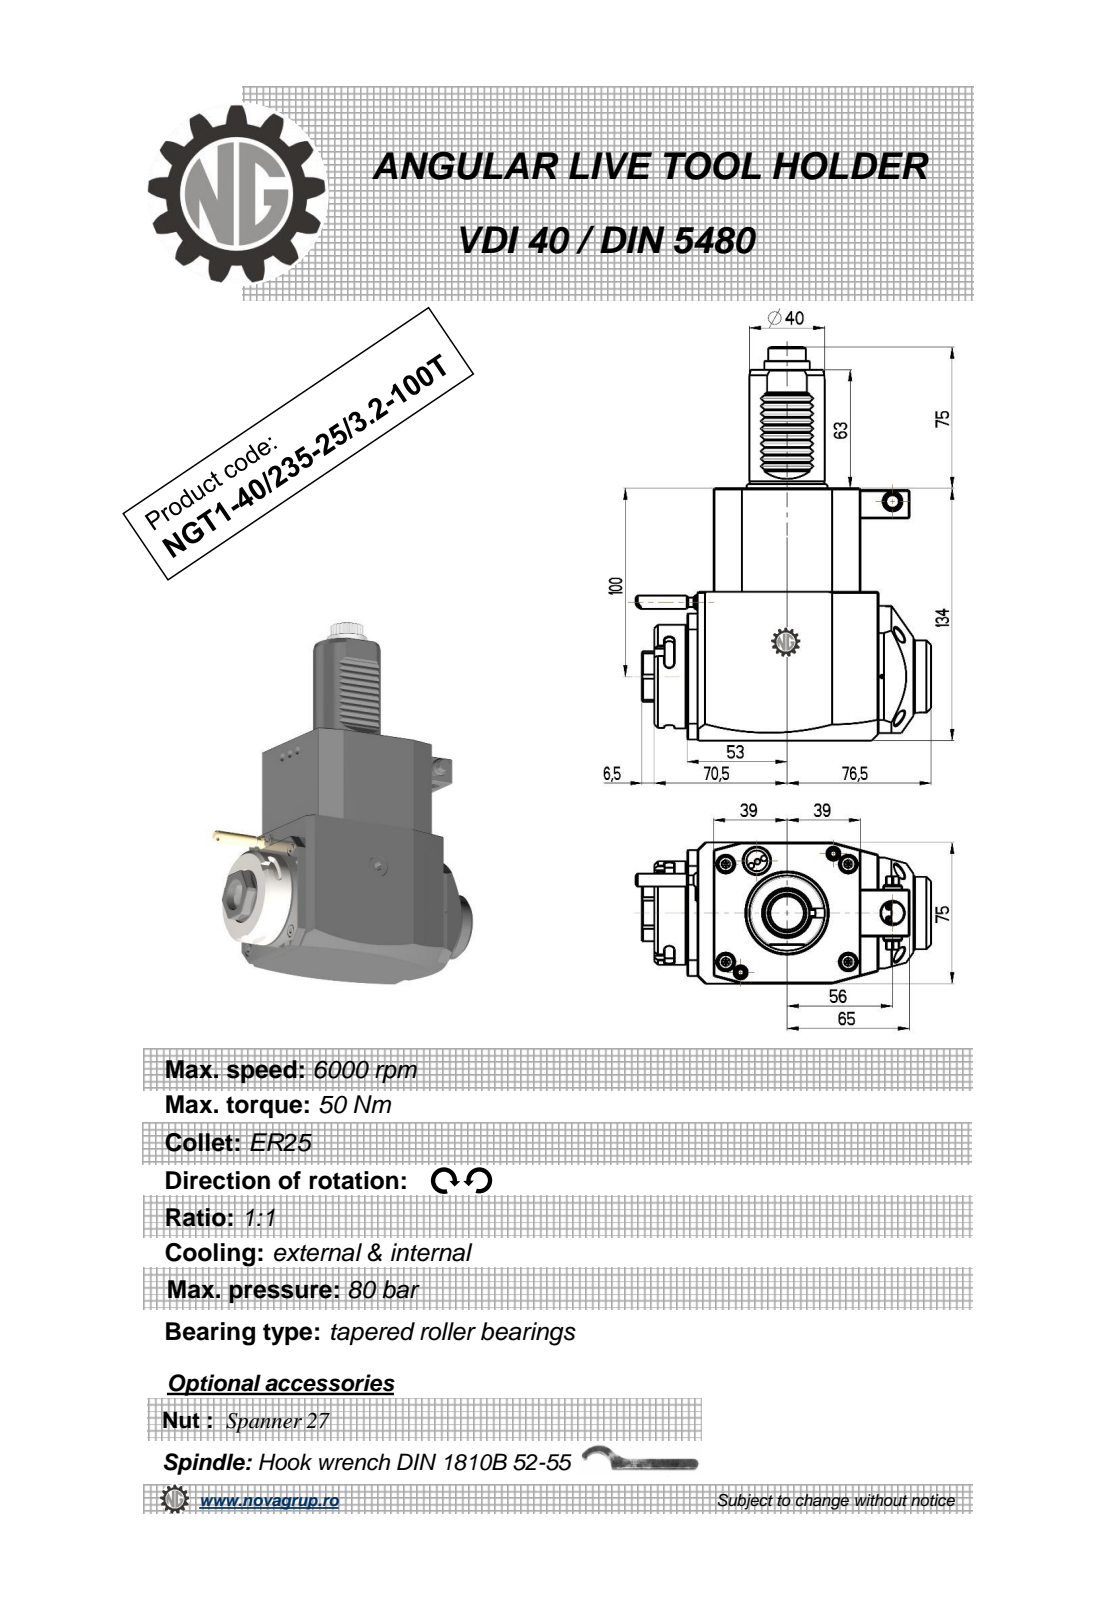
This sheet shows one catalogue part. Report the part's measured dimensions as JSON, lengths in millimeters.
{"part_name": "NGT1_40_235_25_3_2_100T", "step_written_by": "PRO/ENGINEER BY PARAMETRIC TECHNOLOGY CORPORATION, 2010280 (CONFIG_CONTROL_DESIGN)", "units": "millimeters", "bodies": {"solids": 1, "faces": 462, "planar": 186, "cylindrical": 180, "other": 96}, "overall_size": [209, 156.83, 75], "volume_mm3": 1085000, "surface_area_mm2": 77856, "round_holes": [[2.5, 1], [3, 1], [9.5, 1], [12, 1], [18, 1]], "round_bosses_or_shafts": [[8, 2], [55, 1], [48, 1], [40, 1], [38.5, 1], [24, 1], [10, 1], [7, 1]], "partial_cylinders_radius": [[2.08, 48], [0.3, 10], [2.5, 6], [15, 2], [180, 2], [3.85, 1], [4.25, 1], [9.08, 1]], "face_to_face_distances": [75, 134, 78, 14, 92, 17.5, 31.5, 79, 84.88, 109.5], "hole_center_spacings": [43.2, 54.87, 91.5]}
